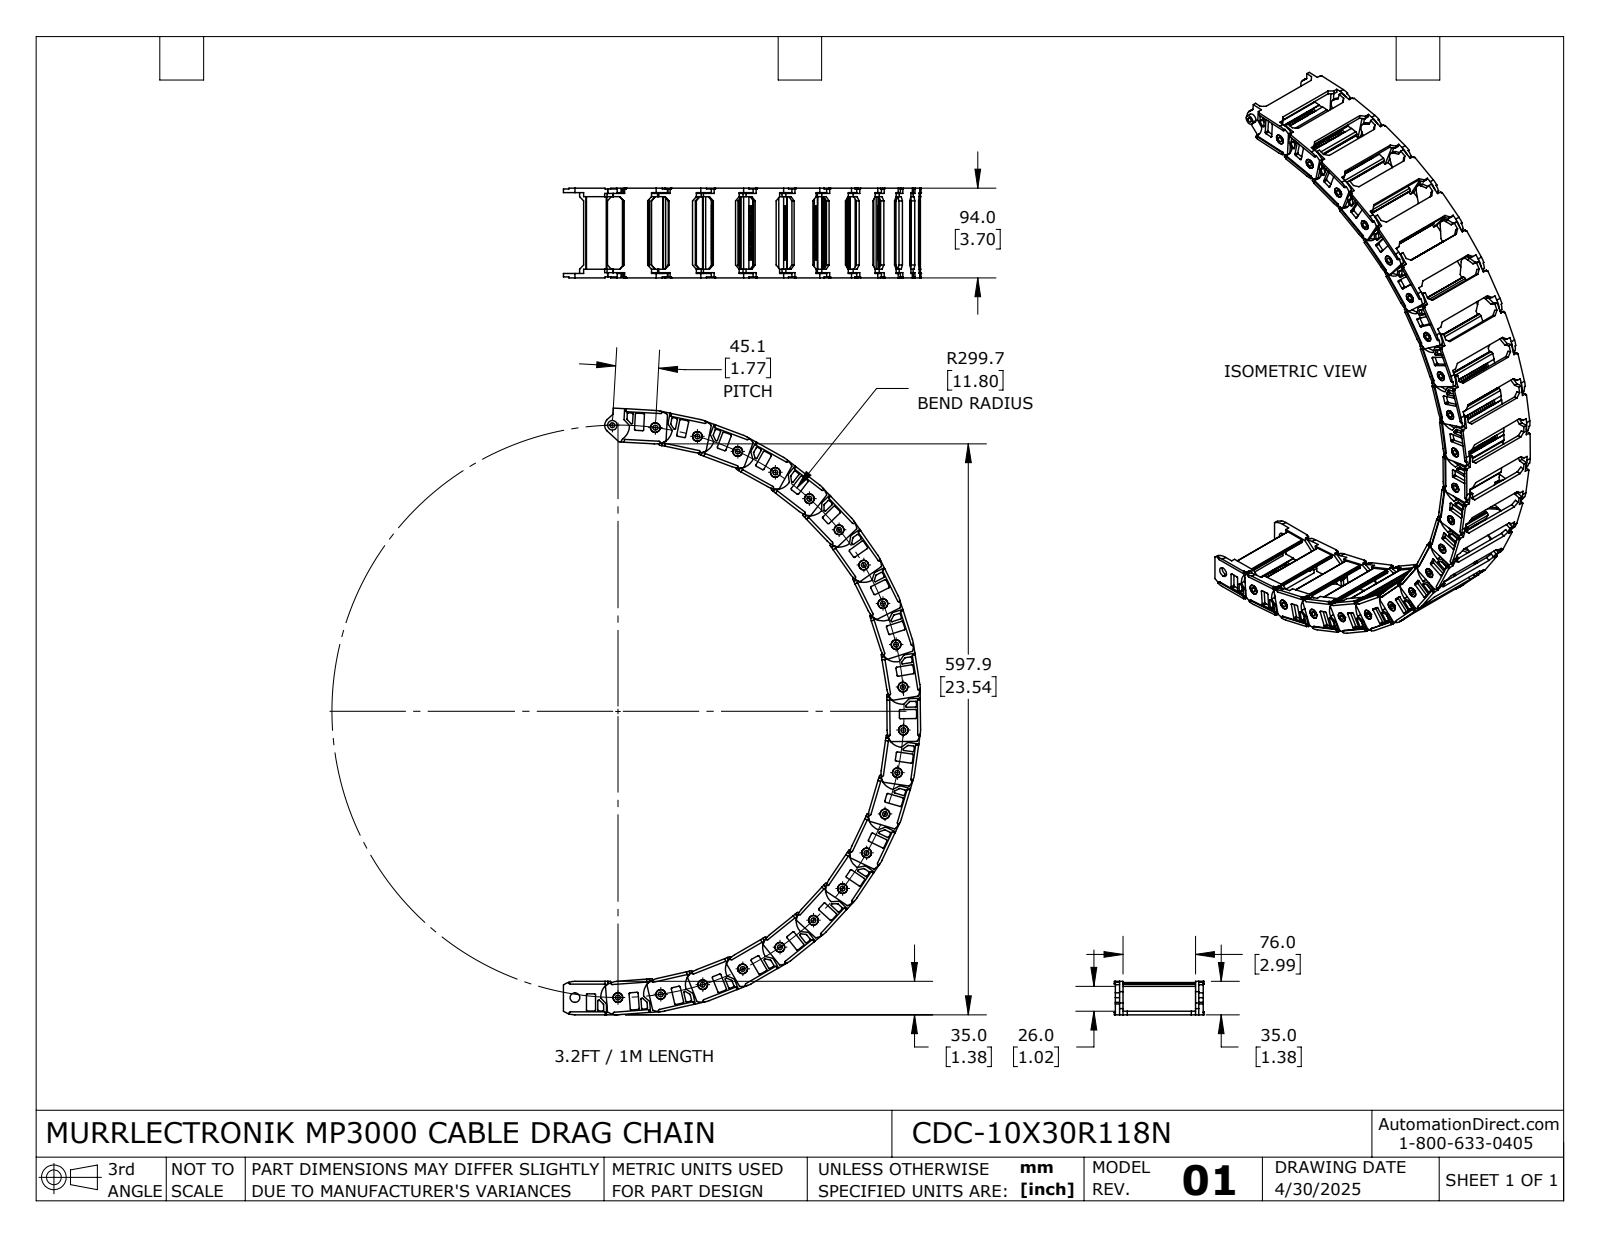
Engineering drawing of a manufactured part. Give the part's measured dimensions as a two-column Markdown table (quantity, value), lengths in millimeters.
| quantity | value |
| --- | --- |
| part name | CDC-10X30R118N |
| STEP written by | SolidWorks 2024 (AUTOMOTIVE_DESIGN) |
| units | millimeters |
| bodies | 22 solids, 4752 faces (3652 planar, 1100 cylindrical, 0 other) |
| overall size | 635.37 × 374.08 × 94 |
| volume | 731 924 mm³ |
| surface area | 448 505 mm² |
| round holes (diameter × count) | 5.1 × 22, 10.1 × 22 |
| round bosses / shafts (diameter × count) | 10 × 22 |
| partial cylindrical surfaces (radius × count) | 1 × 176, 0.5 × 88, 1.5 × 44, 2 × 44, 21 × 44, 2.8 × 22, 8 × 22, 18 × 22 |
| main face-to-face distances | 84, 8, 4, 3.7, 88.3, 4.3, 80.3, 3.5, 76, 0.8 |
| hole center spacings | 134.21, 45.08, 177.76, 89.9, 89.82, 45, 261.6, 45.07 |
